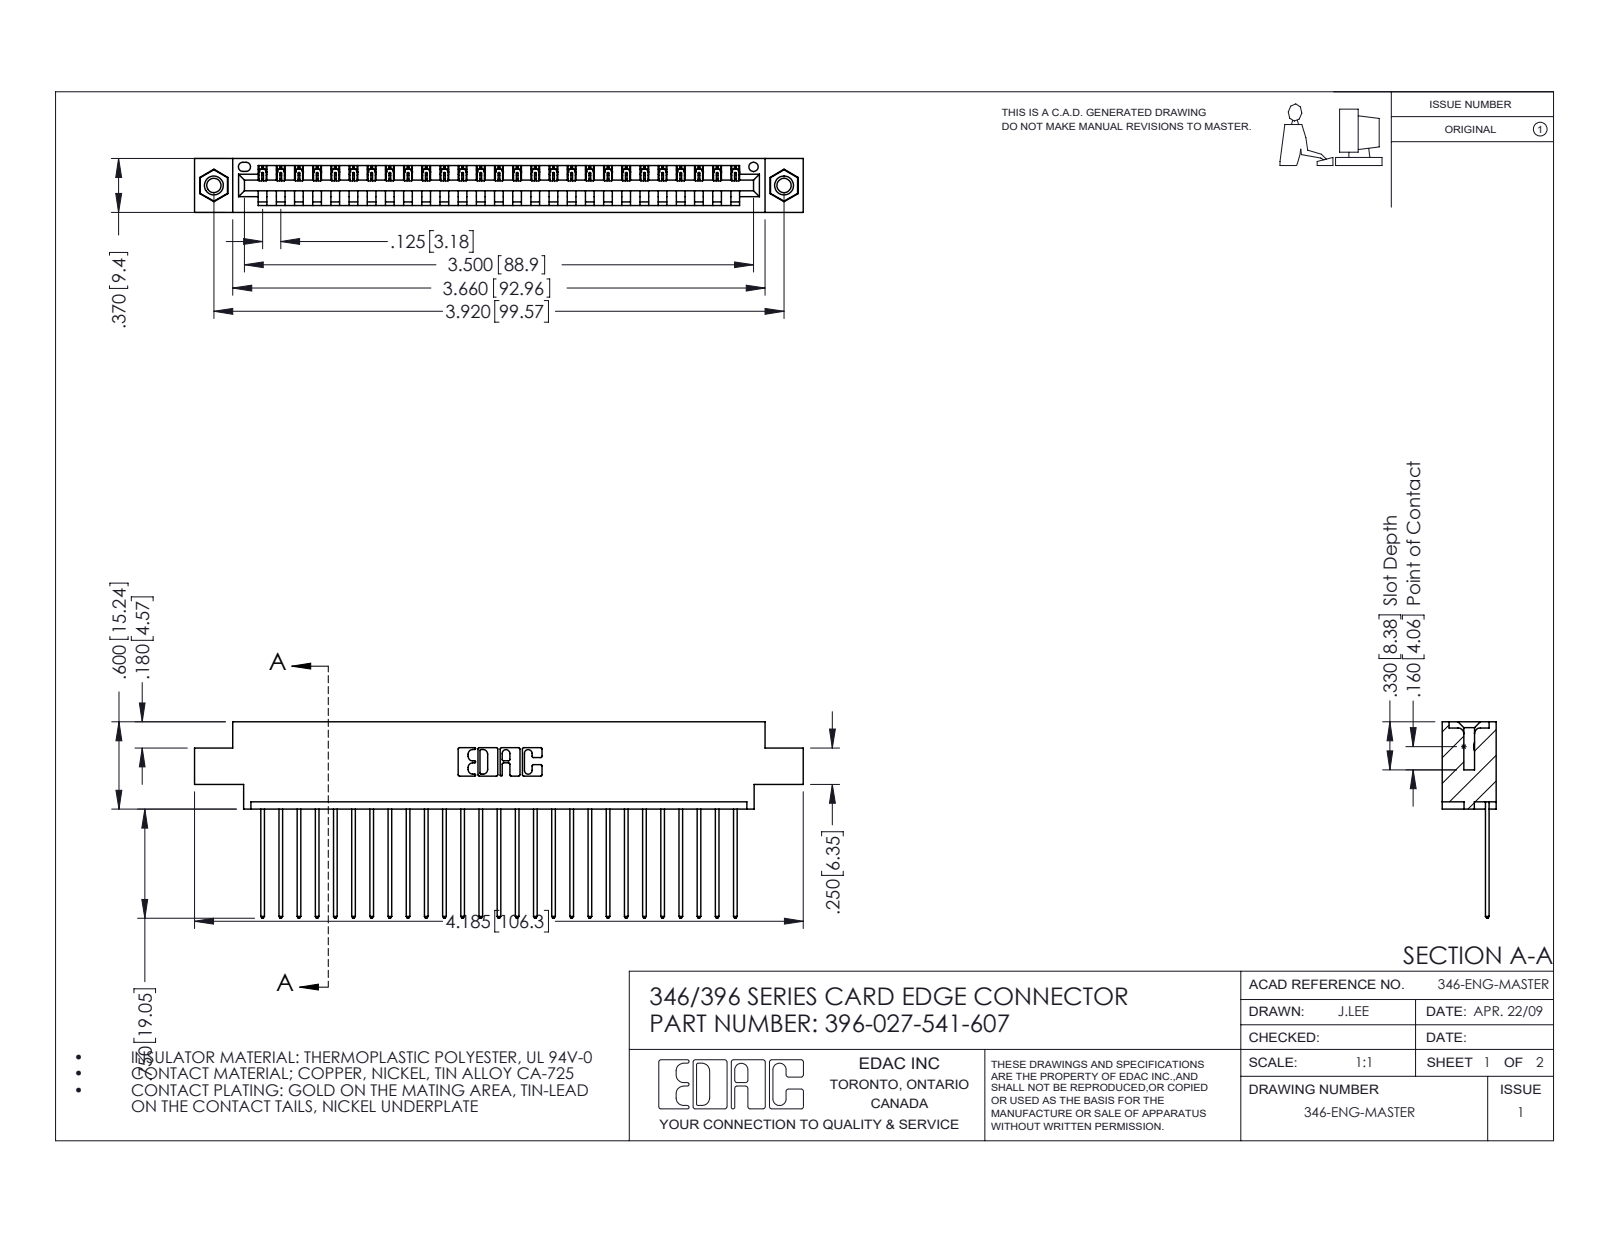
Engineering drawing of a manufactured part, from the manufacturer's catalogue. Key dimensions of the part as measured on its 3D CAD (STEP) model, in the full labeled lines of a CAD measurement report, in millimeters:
Part name (STEP PRODUCT): 346 Part_0.170 Offset - 0.156 Dia-TI; 345-292-001_345-293-141; 396-027-541-607; 345-250-001_345-250-005-103
STEP written by: SolidWorks 2016 (CONFIG_CONTROL_DESIGN)
Units: millimetres
Bodies: 30 solids, 1752 faces (1192 planar, 544 cylindrical, 16 other)
Overall size (bounding box): 106.3 × 34.3 × 9.4
Volume: 10 000 mm³ · Surface area: 13 060 mm²
Round holes (diameter × count): ⌀2.5 ×2, ⌀3.2 ×2, ⌀4 ×2, ⌀1.6 ×1
Round bosses / shafts (diameter × count): ⌀3.9 ×2
Partial cylindrical surfaces — rounded edges, fillets, slot ends (radius × count): R0.2 ×54, R0.3 ×54, R0.3 ×22, R0.2 ×6, R0.8 ×6, R0.7 ×3, R0.8 ×2, R1 ×2
Main face-to-face distances: 1.2, 8.2, 9.4, 6.4, 1.8, 7.6, 0.6, 5.6, 3.8, 2.5
Hole centre spacings: 6.2, 94.3, 99.6
